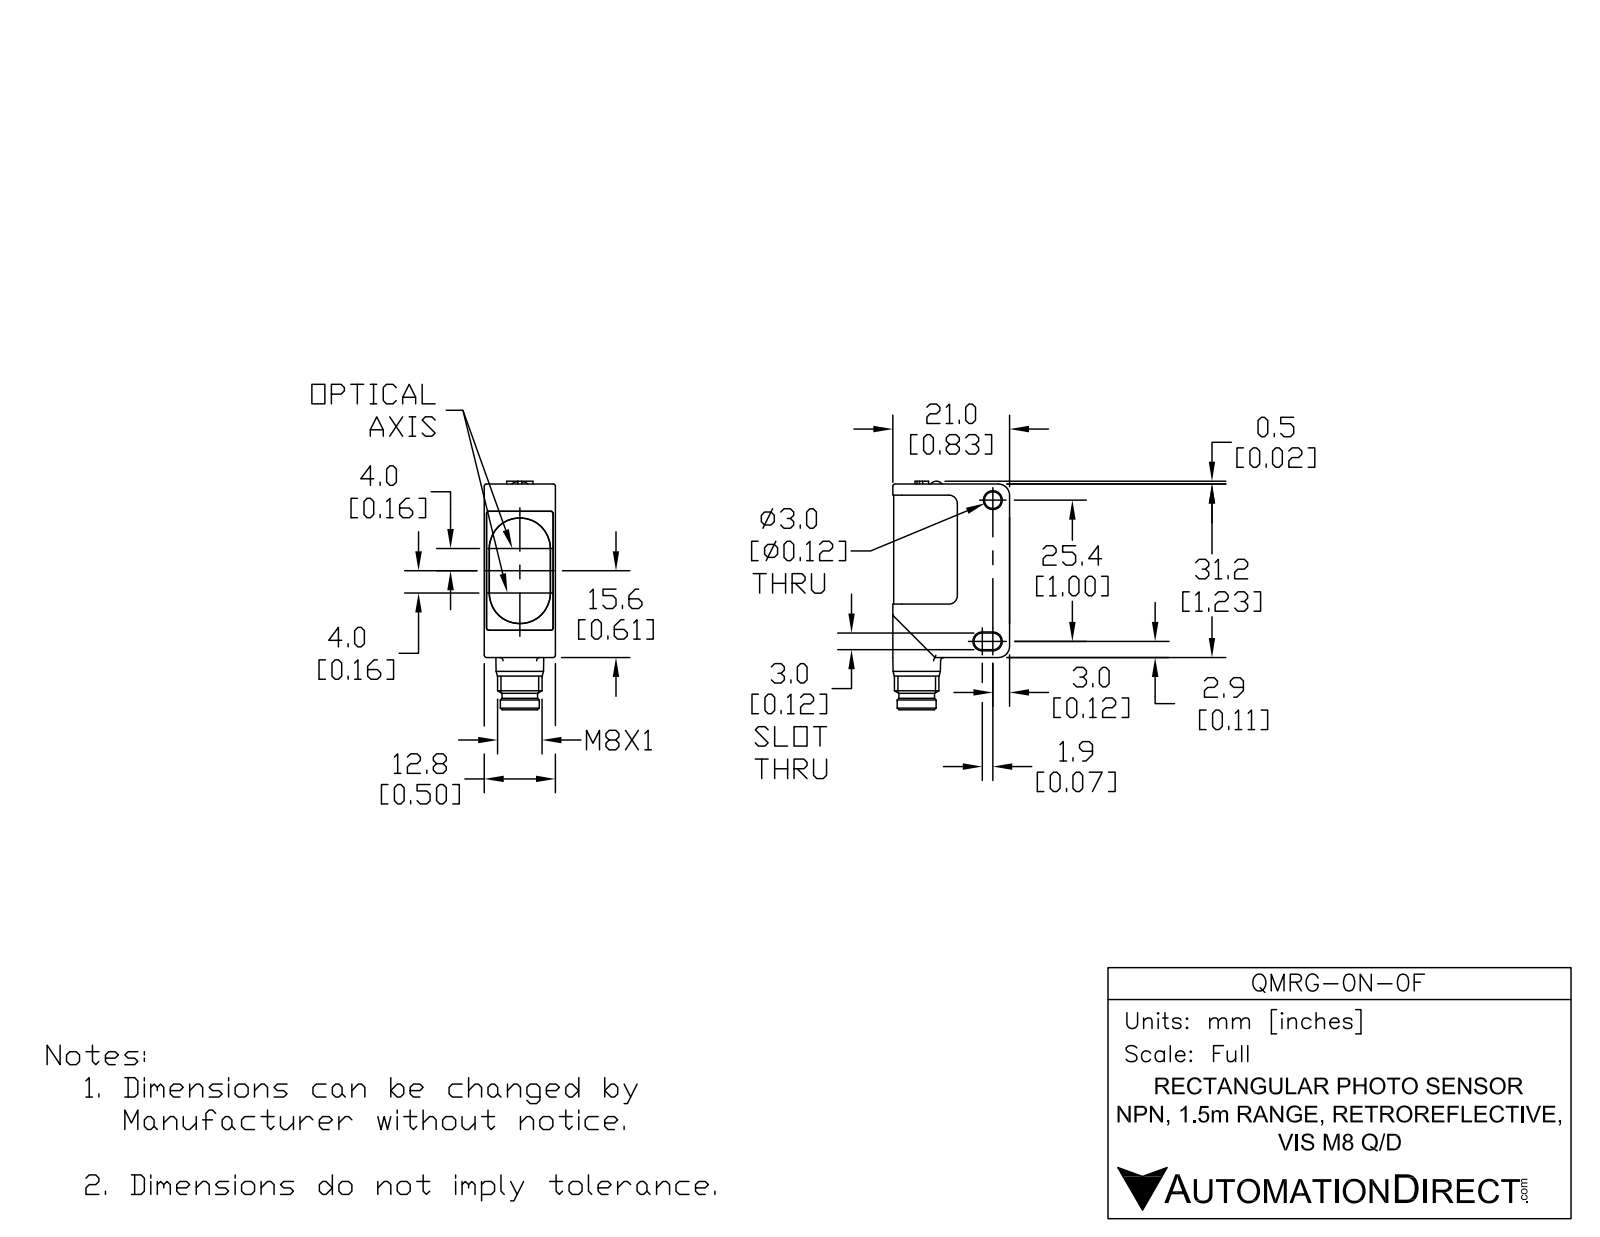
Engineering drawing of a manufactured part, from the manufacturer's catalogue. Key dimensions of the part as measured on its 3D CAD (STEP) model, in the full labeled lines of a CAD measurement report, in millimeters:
Part name (STEP PRODUCT): QMRG-0N-0F
STEP written by: SolidWorks 2017 (AUTOMOTIVE_DESIGN)
Units: millimetres
Bodies: 7 solids, 272 faces (125 planar, 100 cylindrical, 47 other)
Overall size (bounding box): 41.1 × 21 × 12.8
Volume: 7 770 mm³ · Surface area: 4 999 mm²
Round holes (diameter × count): ⌀3 ×3, ⌀5.8 ×1
Round bosses / shafts (diameter × count): ⌀1 ×4, ⌀3.5 ×2, ⌀8 ×1, ⌀7 ×1, ⌀6.4 ×1
Partial cylindrical surfaces — rounded edges, fillets, slot ends (radius × count): R0.4 ×10, R0.5 ×9, R1.5 ×6, R0.6 ×4, R1 ×4, R0.2 ×2, R1.1 ×2, R1.7 ×2
Main face-to-face distances: 12.6, 0.5, 12.8, 2.8, 0.4, 12.5, 12.4, 12.2, 1.5, 18.1
Hole centre spacings: 1, 5.2, 6.2
